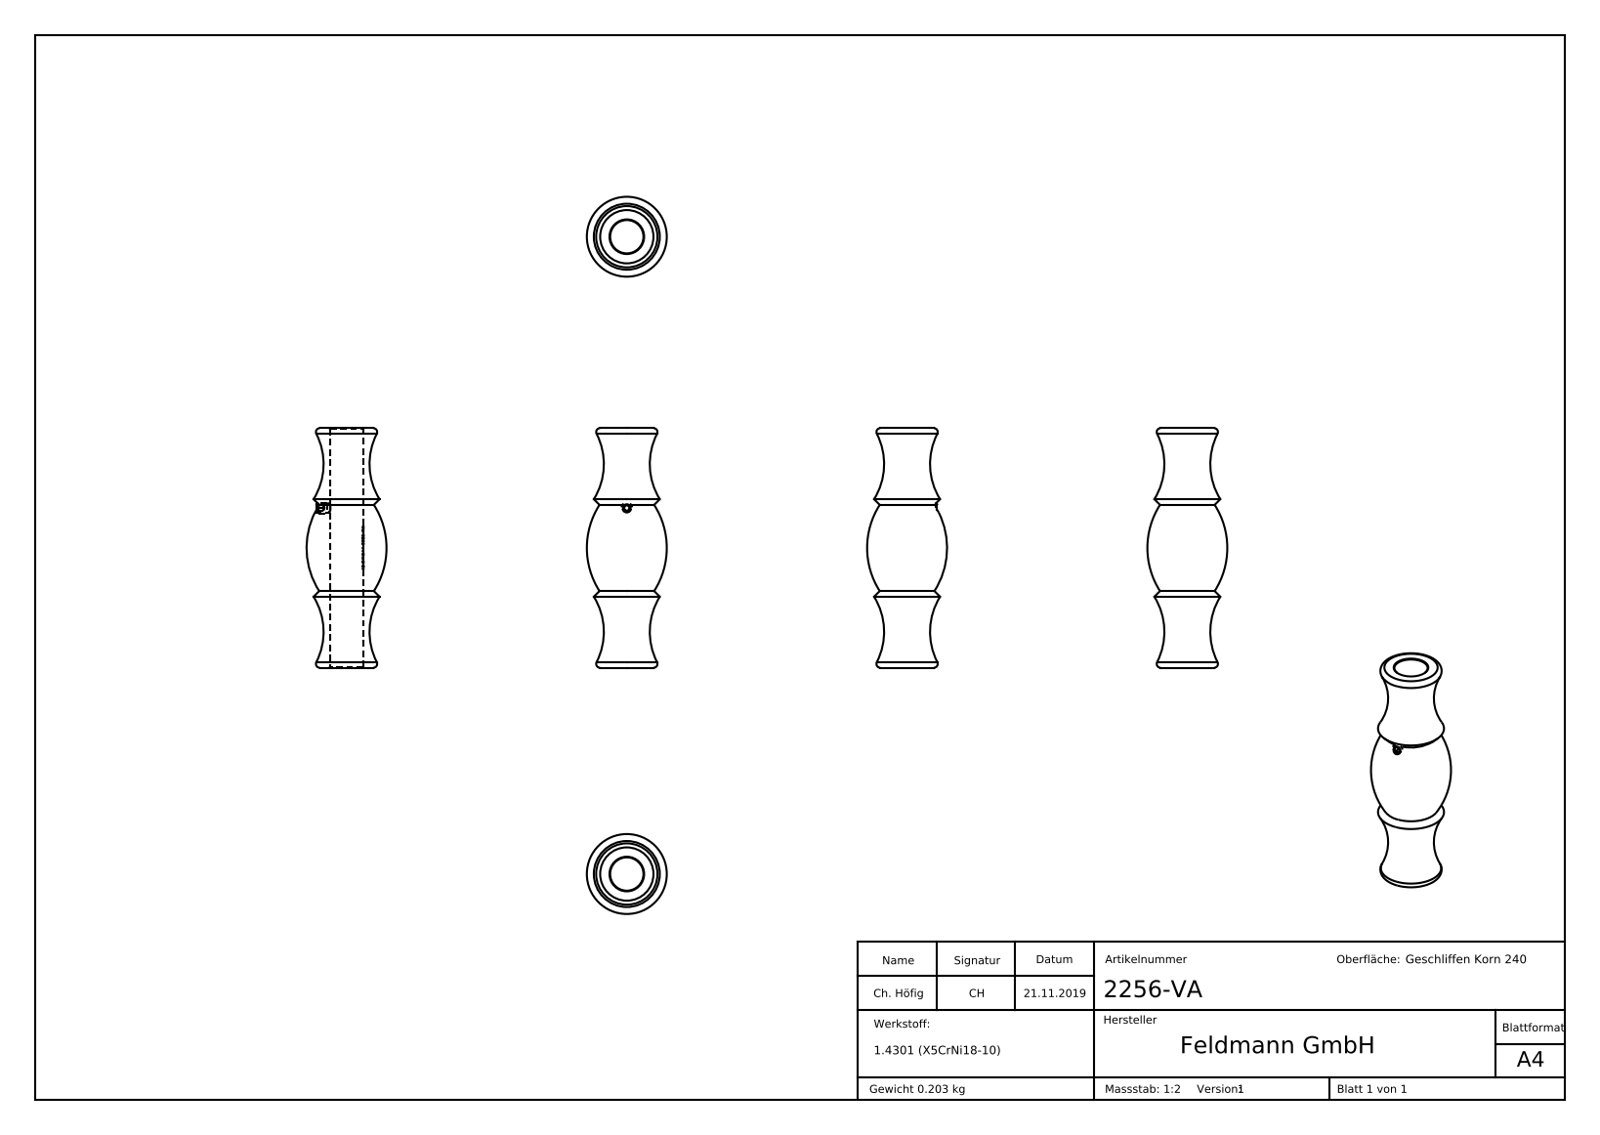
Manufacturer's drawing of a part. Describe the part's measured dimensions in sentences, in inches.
The part is named "2256-VA; 2256-VA Teil1_2256-VA Teil1; DIN913_DIN 913 M4x5; 2256-VA Teil1 (+1 more)". Its 3-D file was written by "SolidWorks 2015 (CONFIG_CONTROL_DESIGN)". It is 2 solids with 225 faces: 113 planar, 23 cylindrical and 89 other. Overall it measures 3.543 by 2.825 by 1.181 inches. Its volume is 1.566 cubic inches and its surface area 16.9 square inches. Round holes: 1 of diameter 0.13, 1 of diameter 0.492. Round bosses or shafts: 1 of diameter 0.157. Partial cylindrical surfaces (rounded edges, fillets, slot ends): 1 of radius 0.25. The main face-to-face distances are 3.543, 0.079, 2.323, 1.22, 2.402, 1.142, 0.197, 0.098, 0.015, 0.052.
